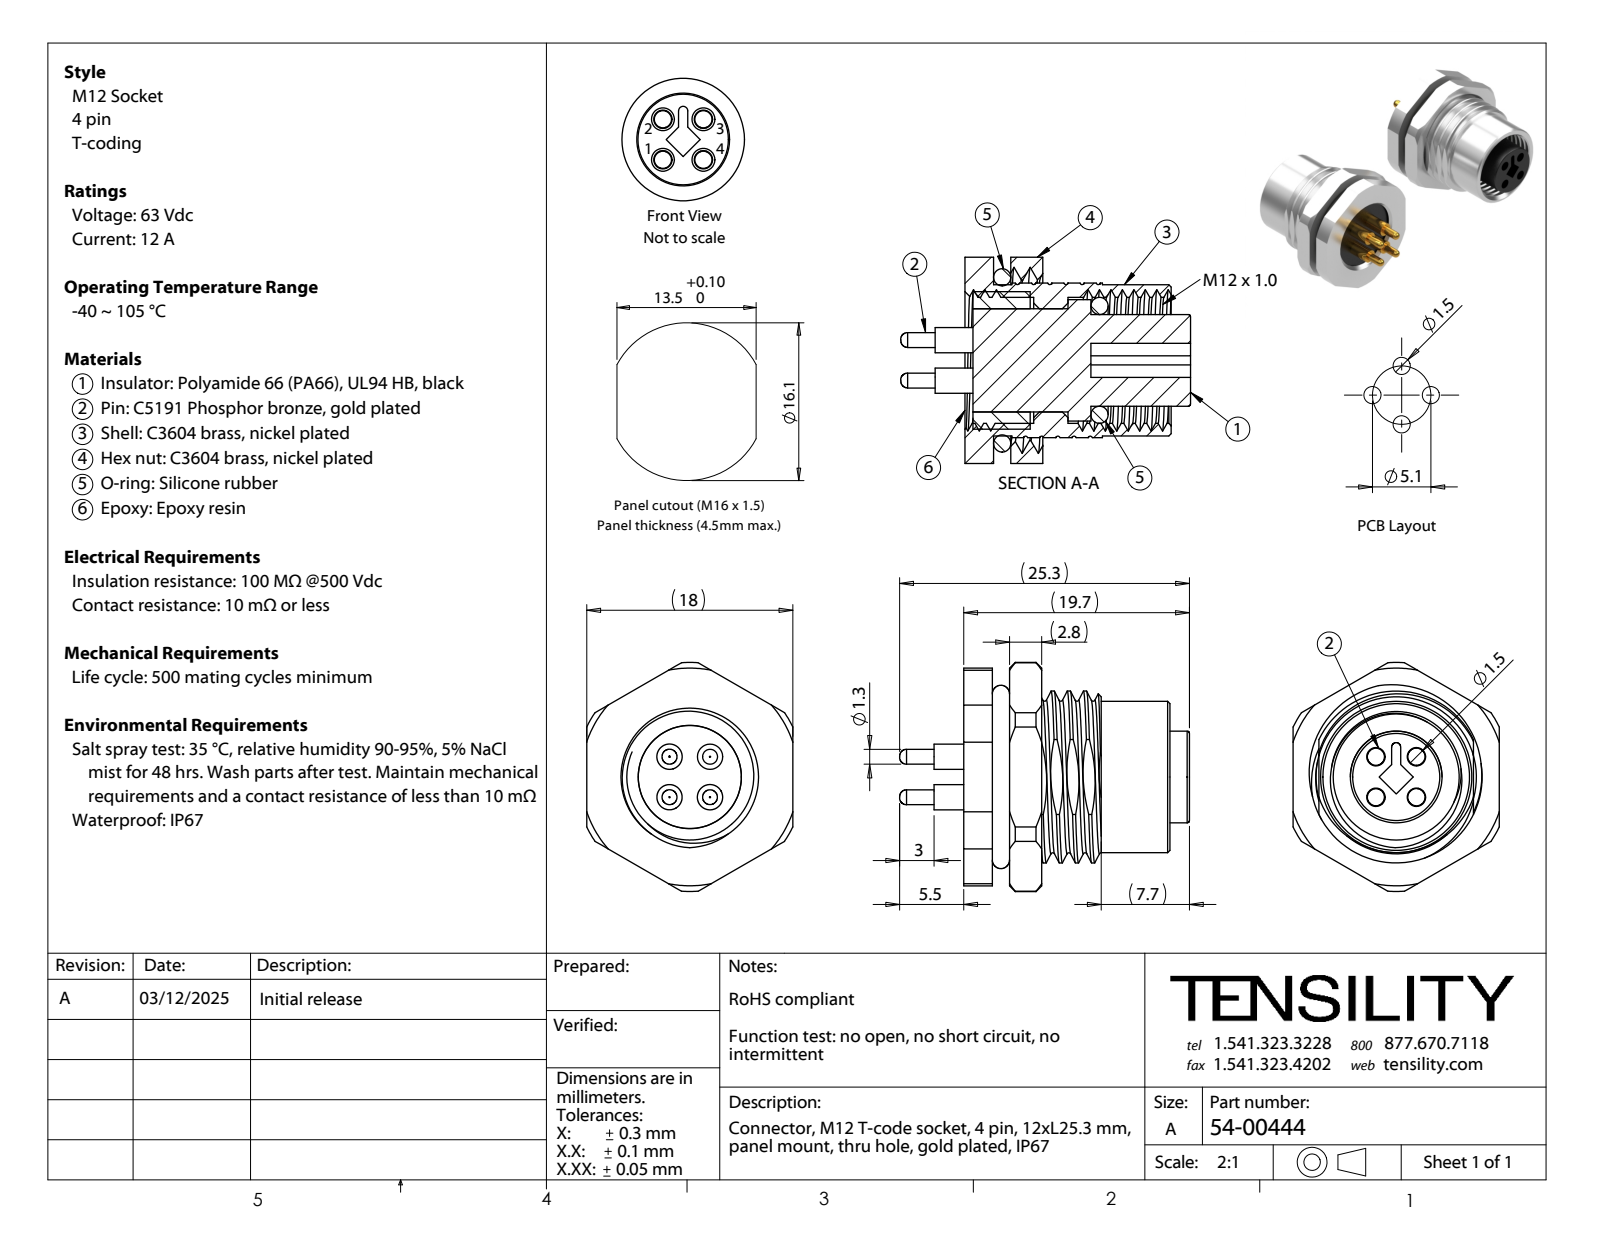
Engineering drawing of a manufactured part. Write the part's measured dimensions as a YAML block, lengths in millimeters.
part_name: "54-00444-06; 54-00444-04; 54-00444; 54-00444-01 (+3 more)"
step_written_by: "SolidWorks 2021 (CONFIG_CONTROL_DESIGN)"
units: millimeters
bodies: {solids: 10, faces: 312, planar: 101, cylindrical: 124, other: 87}
overall_size: [25.3, 19.8, 19.44]
volume: 2948
surface_area: 5770
round_holes:
  - {diameter: 1.5, count: 4}
  - {diameter: 1.6, count: 4}
  - {diameter: 9, count: 1}
  - {diameter: 11, count: 1}
  - {diameter: 14, count: 1}
round_bosses_or_shafts:
  - {diameter: 2.2, count: 4}
  - {diameter: 1.3, count: 4}
  - {diameter: 13.2, count: 1}
  - {diameter: 12, count: 1}
  - {diameter: 10.6, count: 1}
  - {diameter: 8, count: 1}
partial_cylinders:
  - {radius: 0.4, count: 1}
  - {radius: 7.5, count: 1}
  - {radius: 9.5, count: 1}
  - {radius: 10, count: 1}
face_to_face_distances: [2.5, 3.3, 18, 5, 0.7, 1.8, 4, 4.3, 1.5, 6.8]
hole_center_spacings: [2.5, 3.54, 5.01]
